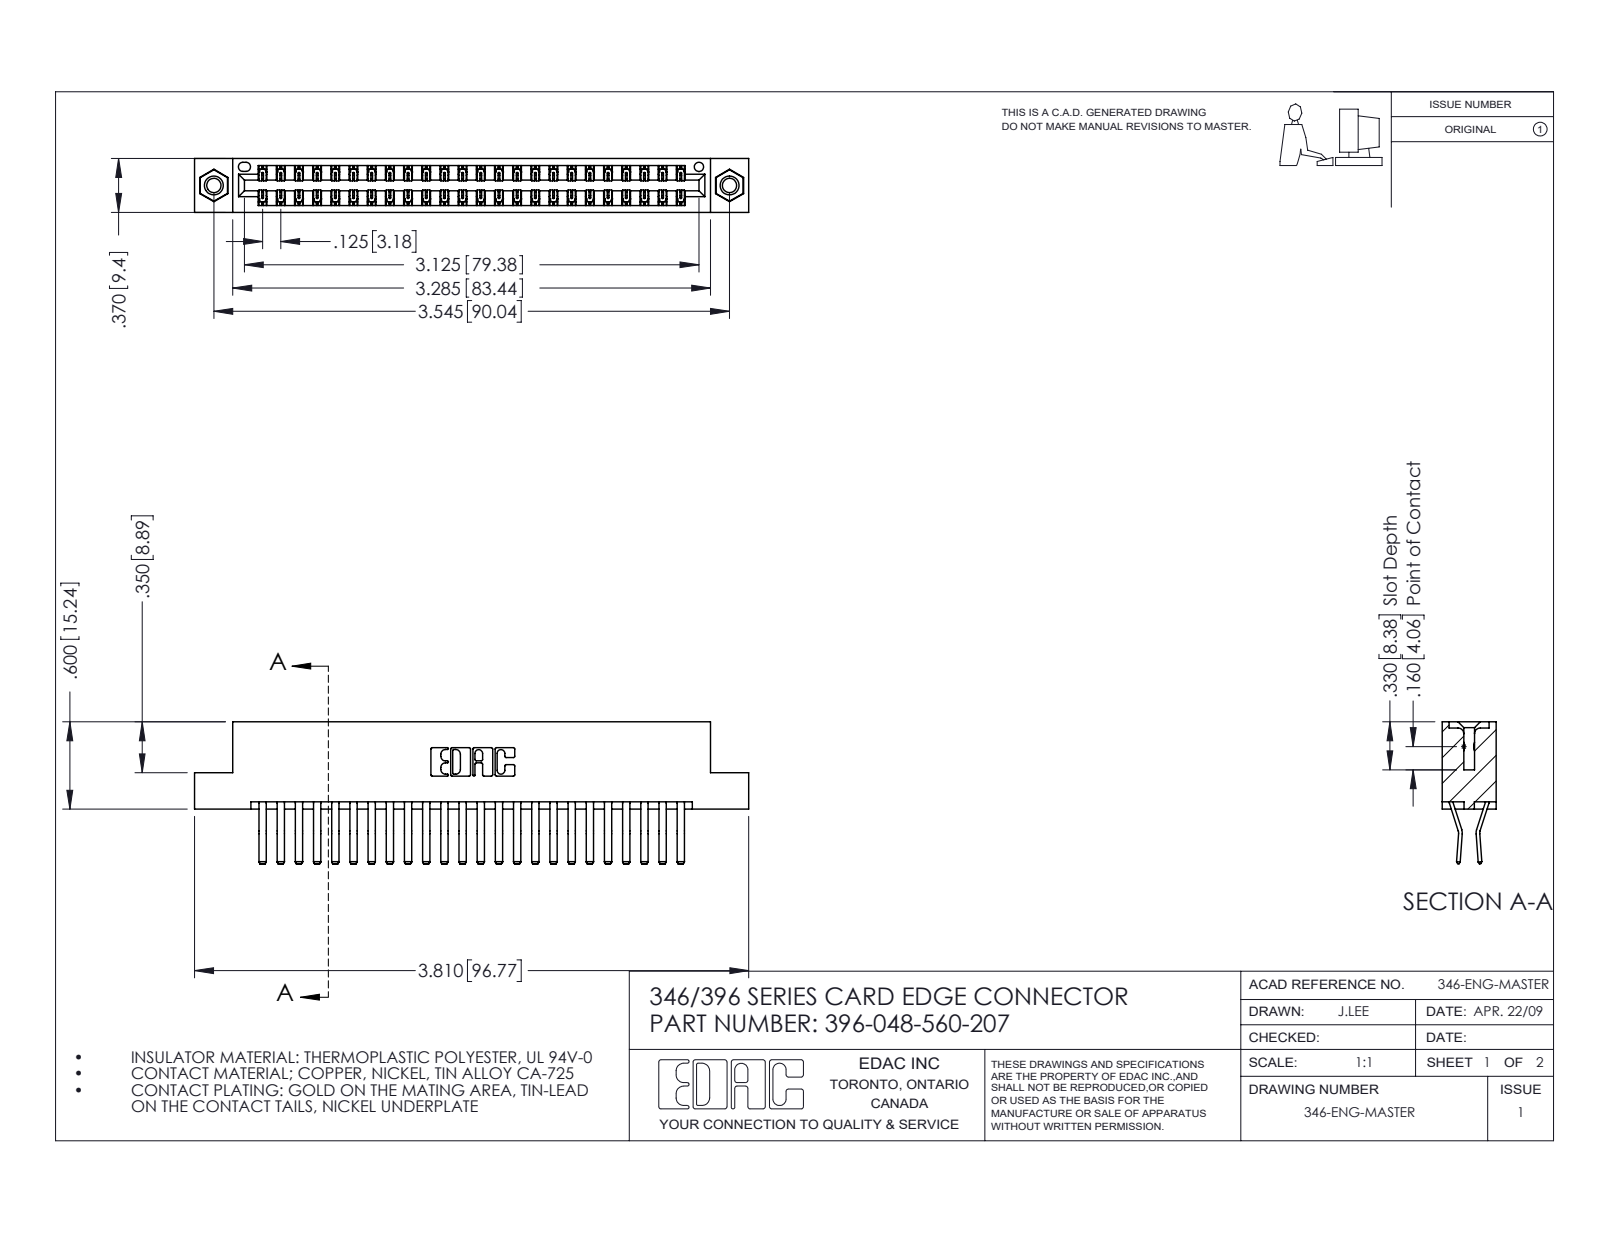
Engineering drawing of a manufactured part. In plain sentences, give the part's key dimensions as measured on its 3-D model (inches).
The part is named "396-048-560-207; 345-250-001_345-250-005-103; 345-292-001_560 Tail; 346 Part_Flush Mounting Lugs - 0.156 Dia-TI". Its 3-D file was written by "SolidWorks 2016 (CONFIG_CONTROL_DESIGN)". It is 51 solids with 2774 faces: 1788 planar, 970 cylindrical and 16 other. Overall it measures 3.81 by 0.975 by 0.37 inches. Its volume is 0.586 cubic inches and its surface area 21.36 square inches. Round holes: 2 of diameter 0.098, 2 of diameter 0.125, 2 of diameter 0.156, 1 of diameter 0.064. Round bosses or shafts: 2 of diameter 0.155. Partial cylindrical surfaces (rounded edges, fillets, slot ends): 72 of radius 0.006, 22 of radius 0.01, 6 of radius 0.007, 6 of radius 0.031, 3 of radius 0.026, 2 of radius 0.01, 2 of radius 0.014, 2 of radius 0.022. The main face-to-face distances are 0.048, 0.322, 0.37, 0.25, 0.025, 0.072, 0.298, 0.275, 0.148, 0.222. The hole center spacings are 0.246, 3.337, 3.545.
